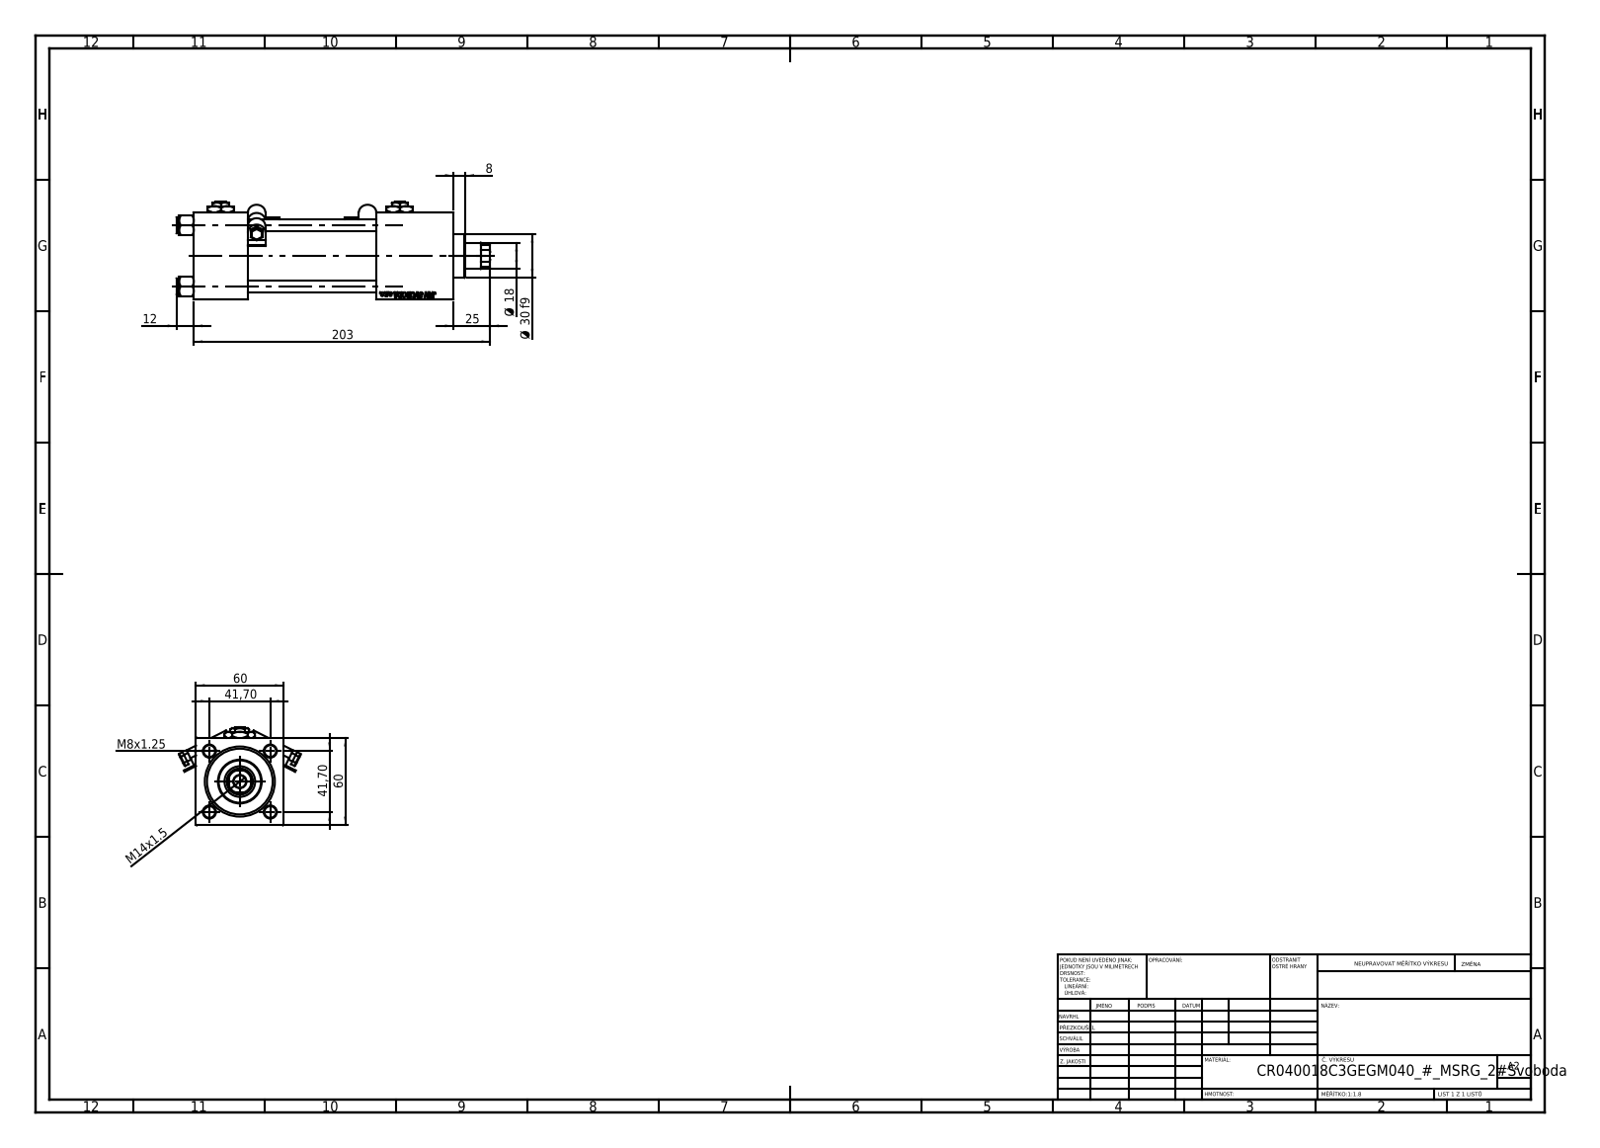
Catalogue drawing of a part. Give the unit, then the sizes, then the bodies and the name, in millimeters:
Units: millimetres
Overall size (bounding box): 215 × 83.44 × 67
Round holes (diameter × count): ⌀8 ×4, ⌀7 ×2, ⌀16.66 ×2, ⌀24 ×2, ⌀8.5 ×1, ⌀18 ×1, ⌀21 ×1, ⌀31 ×1, ⌀40 ×1, ⌀45 ×1
Round bosses / shafts (diameter × count): ⌀11 ×4, ⌀5 ×2, ⌀2.5 ×2, ⌀46 ×1, ⌀30 ×1
Partial cylindrical surfaces — rounded edges, fillets, slot ends (radius × count): R0.5 ×12, R6 ×4, R8.5 ×1
Main face-to-face distances: 60, 37, 125, 53, 178, 141, 88, 149.3, 112.3, 24.3
Hole centre spacings: 29.49, 41.7, 58.97, 122.5
Volume: 431 739 mm³ · Surface area: 125 446 mm²
Bodies: 15 solids, 1314 faces (610 planar, 126 cylindrical, 578 other)
Part name (STEP PRODUCT): V215CR_C_Body; NUT_M5_C; V215CR_VCP_C; V215_VC_A (+3 more)
STEP written by: SolidWorks 2019 (CONFIG_CONTROL_DESIGN)
